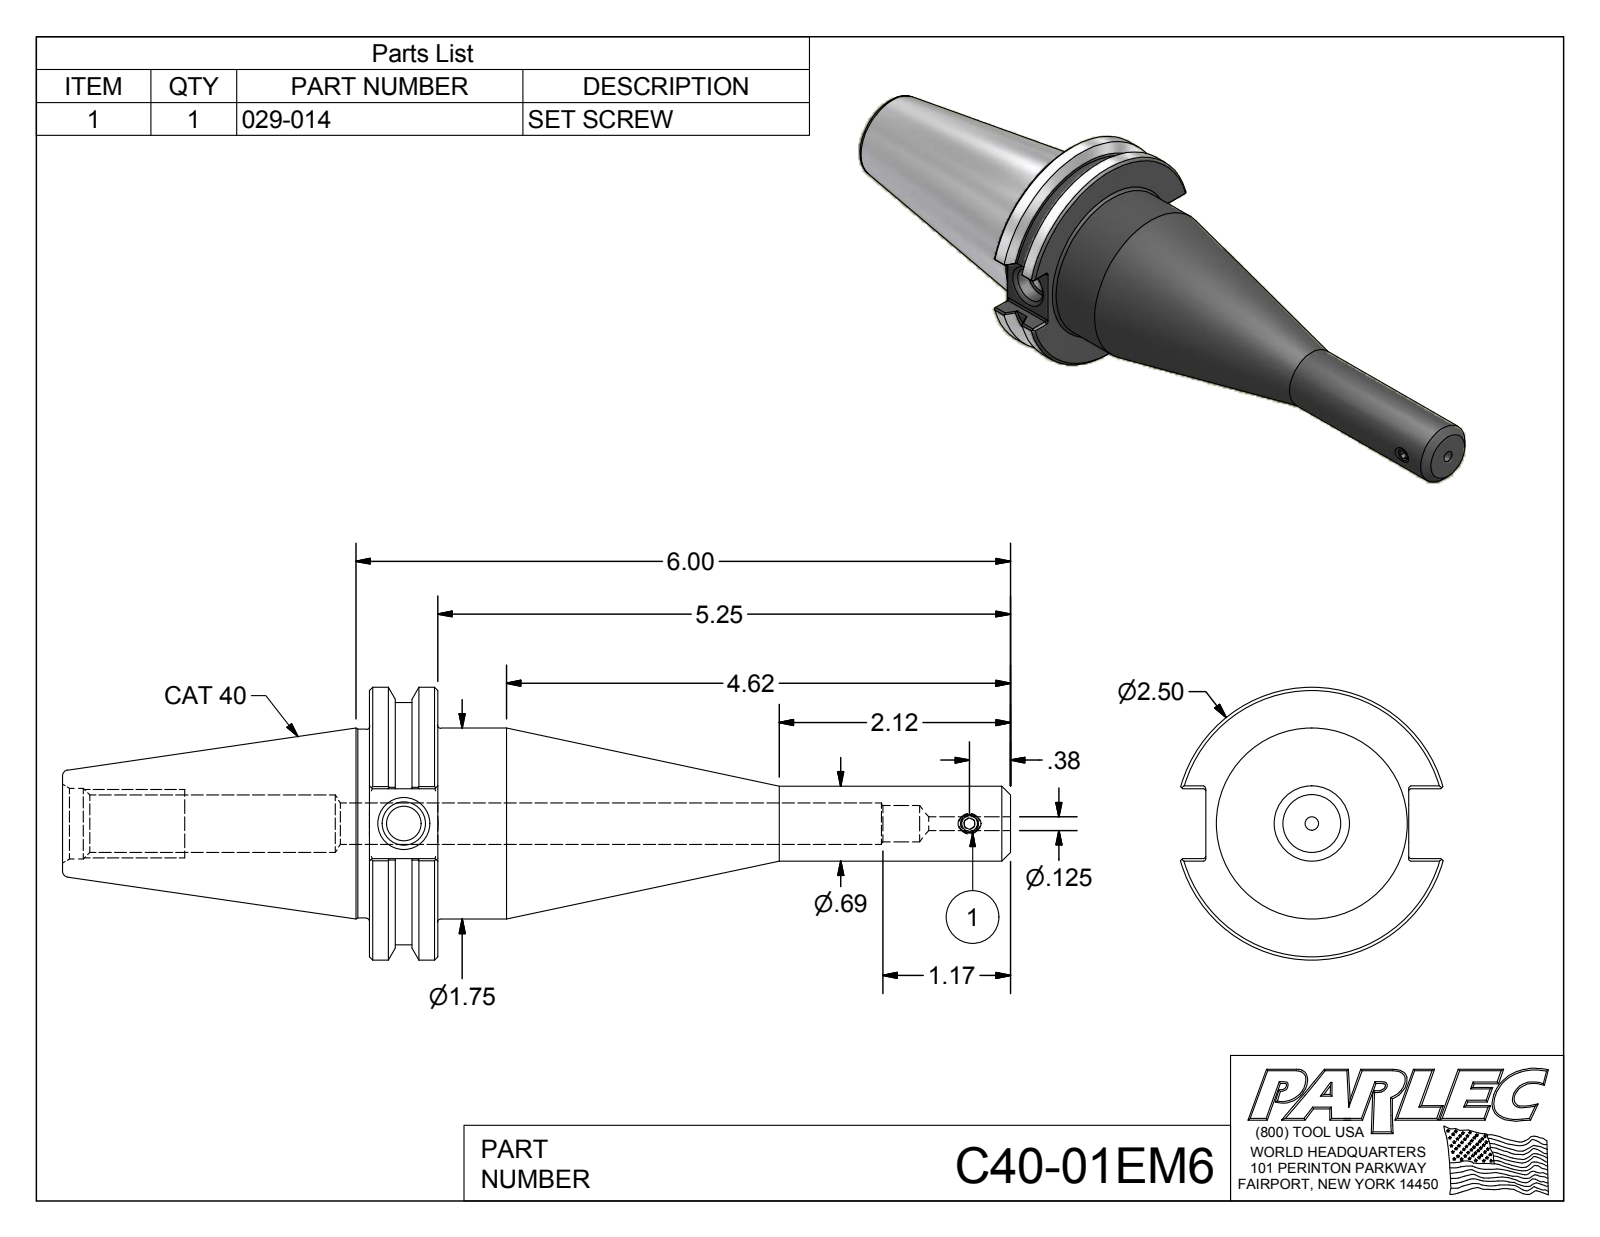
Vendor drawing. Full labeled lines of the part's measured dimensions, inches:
Part name (STEP PRODUCT): C40-01EM6; C40-01EM6-1; 029-014
STEP written by: Autodesk Inventor 2012 (AUTOMOTIVE_DESIGN)
Units: inches
Bodies: 2 solids, 105 faces (40 planar, 30 cylindrical, 35 other)
Overall size (bounding box): 8.687 × 2.5 × 2.406
Volume: 11.11 in³ · Surface area: 52.67 in²
Round holes (diameter × count): ⌀0.125 ×1, ⌀0.145 ×1, ⌀0.315 ×1, ⌀0.332 ×1, ⌀0.38 ×1, ⌀0.399 ×1, ⌀0.527 ×1, ⌀0.648 ×1
Round bosses / shafts (diameter × count): ⌀2.5 ×1, ⌀2.219 ×1, ⌀1.75 ×1, ⌀1.73 ×1, ⌀0.687 ×1, ⌀0.19 ×1
Partial cylindrical surfaces — rounded edges, fillets, slot ends (radius × count): R0.02 ×12
Main face-to-face distances: 0.625, 0.64, 5.875, 5.25, 1.86, 2.812, 3.437, 8.687, 3.201, 0.389
Hole centre spacings: 5.185
